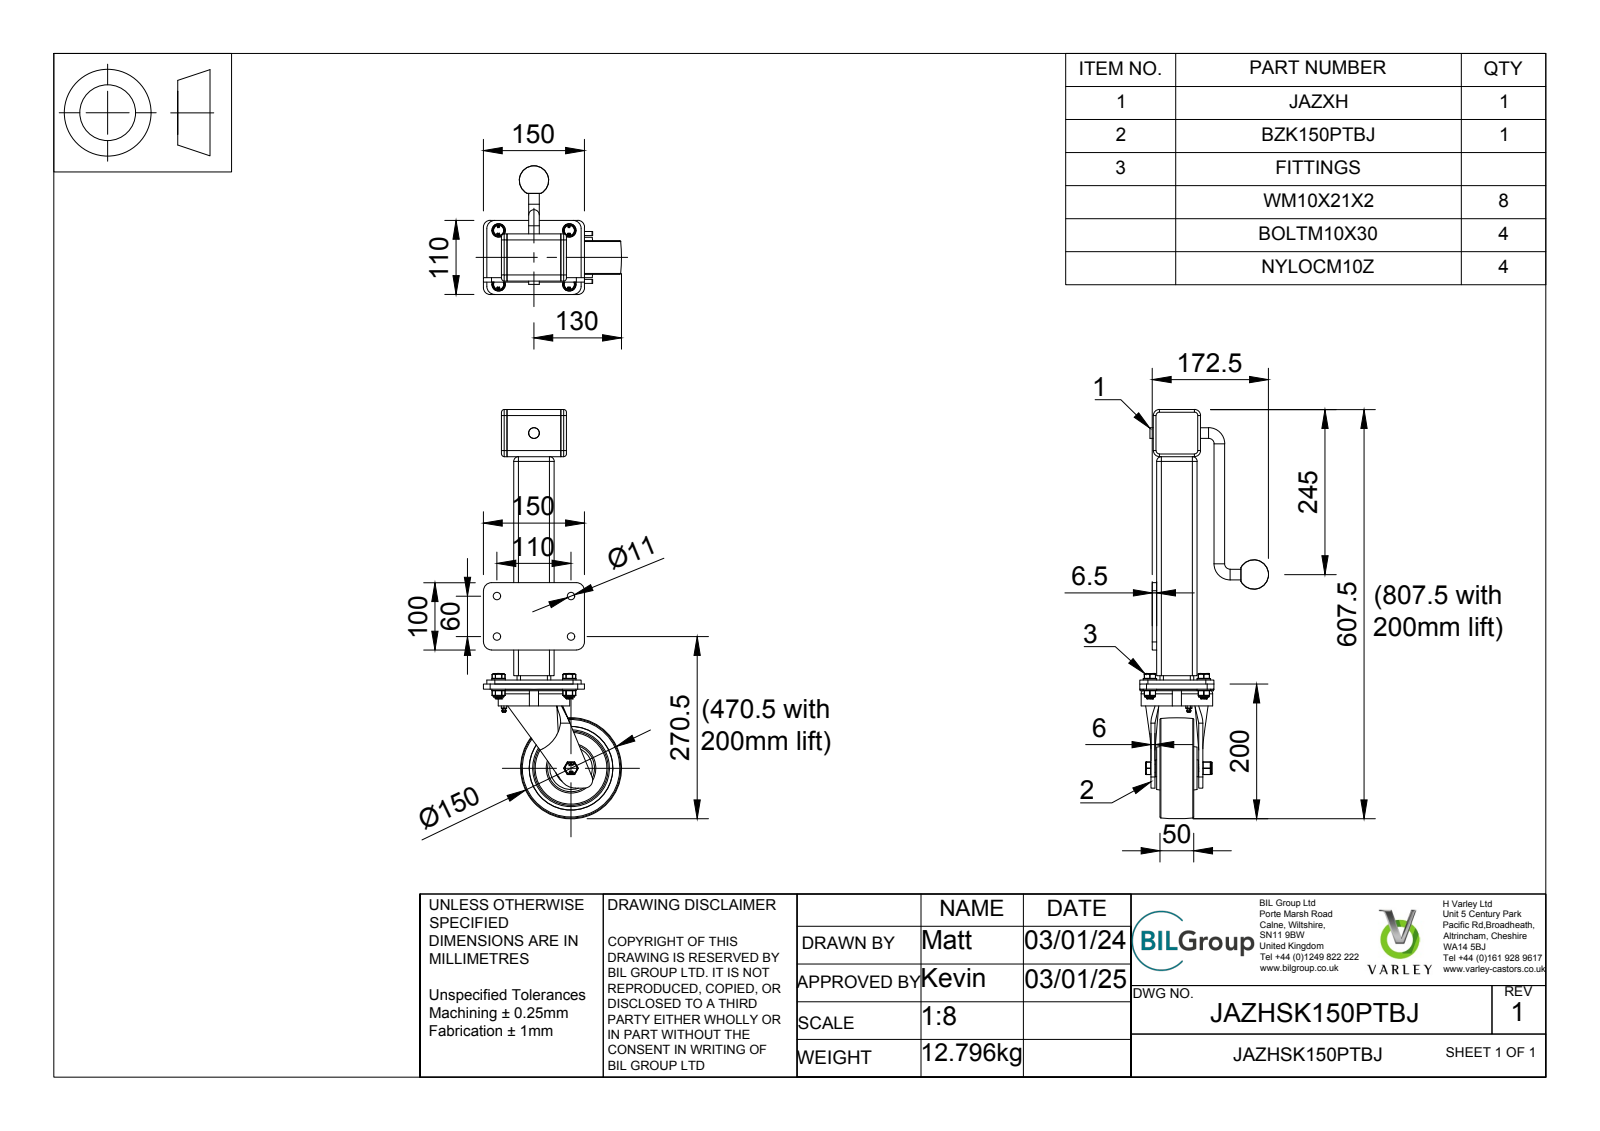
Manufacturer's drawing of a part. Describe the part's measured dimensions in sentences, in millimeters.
The part is named "JAZHSK150PTBJ v4; BZK150AS v1; FABRICATED STEEL TOP PLATE; FABRICATED STEEL FORKS (+8 more)". Its 3-D file was written by "Autodesk Translation Framework v13.20.0.188 (AP242_MANAGED_MODEL_BASED_3D_ENGINEERING_MIM_LF)". It is 65 solids with 2350 faces: 972 planar, 713 cylindrical and 665 other. Overall it measures 607.5 by 205 by 191 millimeters. Its volume is 1 900 000 cubic millimeters and its surface area 723 218 square millimeters. Round holes: 5 of diameter 12, 4 of diameter 10, 4 of diameter 10.5, 4 of diameter 11, 1 of diameter 12.2, 1 of diameter 13, 1 of diameter 14, 1 of diameter 15.75, 1 of diameter 16, 1 of diameter 20, 1 of diameter 28.5, 1 of diameter 41.5. Round bosses or shafts: 4 of diameter 20, 4 of diameter 16, 4 of diameter 9.85, 4 of diameter 8.14, 2 of diameter 15.75, 1 of diameter 109, 1 of diameter 107, 1 of diameter 40.5. Partial cylindrical surfaces (rounded edges, fillets, slot ends): 91 of radius 0.5, 18 of radius 4, 16 of radius 0.33, 16 of radius 0.64, 16 of radius 7, 14 of radius 6, 9 of radius 12, 8 of radius 0.63. The main face-to-face distances are 5, 3, 52, 57, 2, 8, 55, 49, 47, 60. The hole center spacings are 66, 60, 63.63, 80, 105, 107.19, 110, 125.3.
